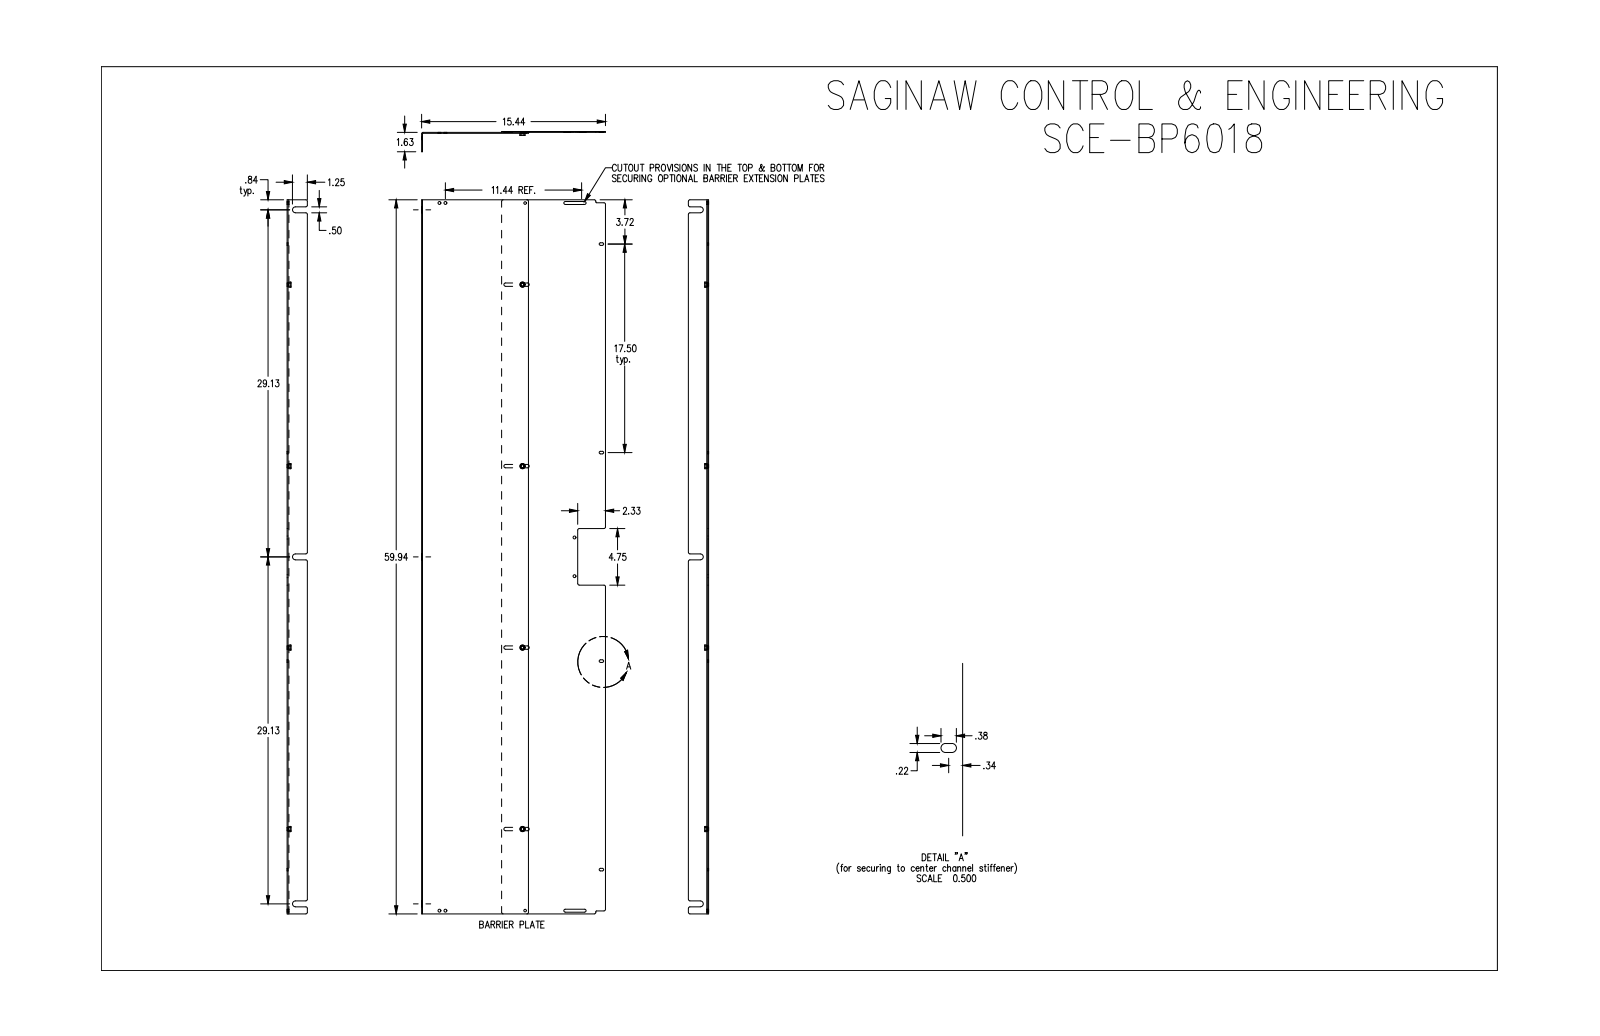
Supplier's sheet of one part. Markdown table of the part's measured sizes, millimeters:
| quantity | value |
| --- | --- |
| part name | SCE-BP6018 |
| STEP written by | SolidWorks 2019 (CONFIG_CONTROL_DESIGN) |
| units | millimeters |
| bodies | 6 solids, 146 faces (63 planar, 71 cylindrical, 12 other) |
| overall size | 1522.4 × 392.2 × 43.2 |
| volume | 1 395 000 mm³ |
| surface area | 1 480 000 mm² |
| round holes (diameter × count) | 6.4 × 10, 8.7 × 4, 5.5 × 2 |
| round bosses / shafts (diameter × count) | 11.2 × 4, 8.7 × 4 |
| partial cylindrical surfaces (radius × count) | 3.2 × 24, 2.8 × 8, 3.6 × 8, 6.4 × 3, 1.6 × 2, 1.1 × 1, 3 × 1 |
| main face-to-face distances | 1.9, 3.8, 170.7, 227.8, 168.8, 225.9, 57.2, 43.2, 41.3, 39.4 |
| hole center spacings | 386.8, 12.7, 169.9, 173.9, 182.6, 188.3, 239.4, 248.3 |
